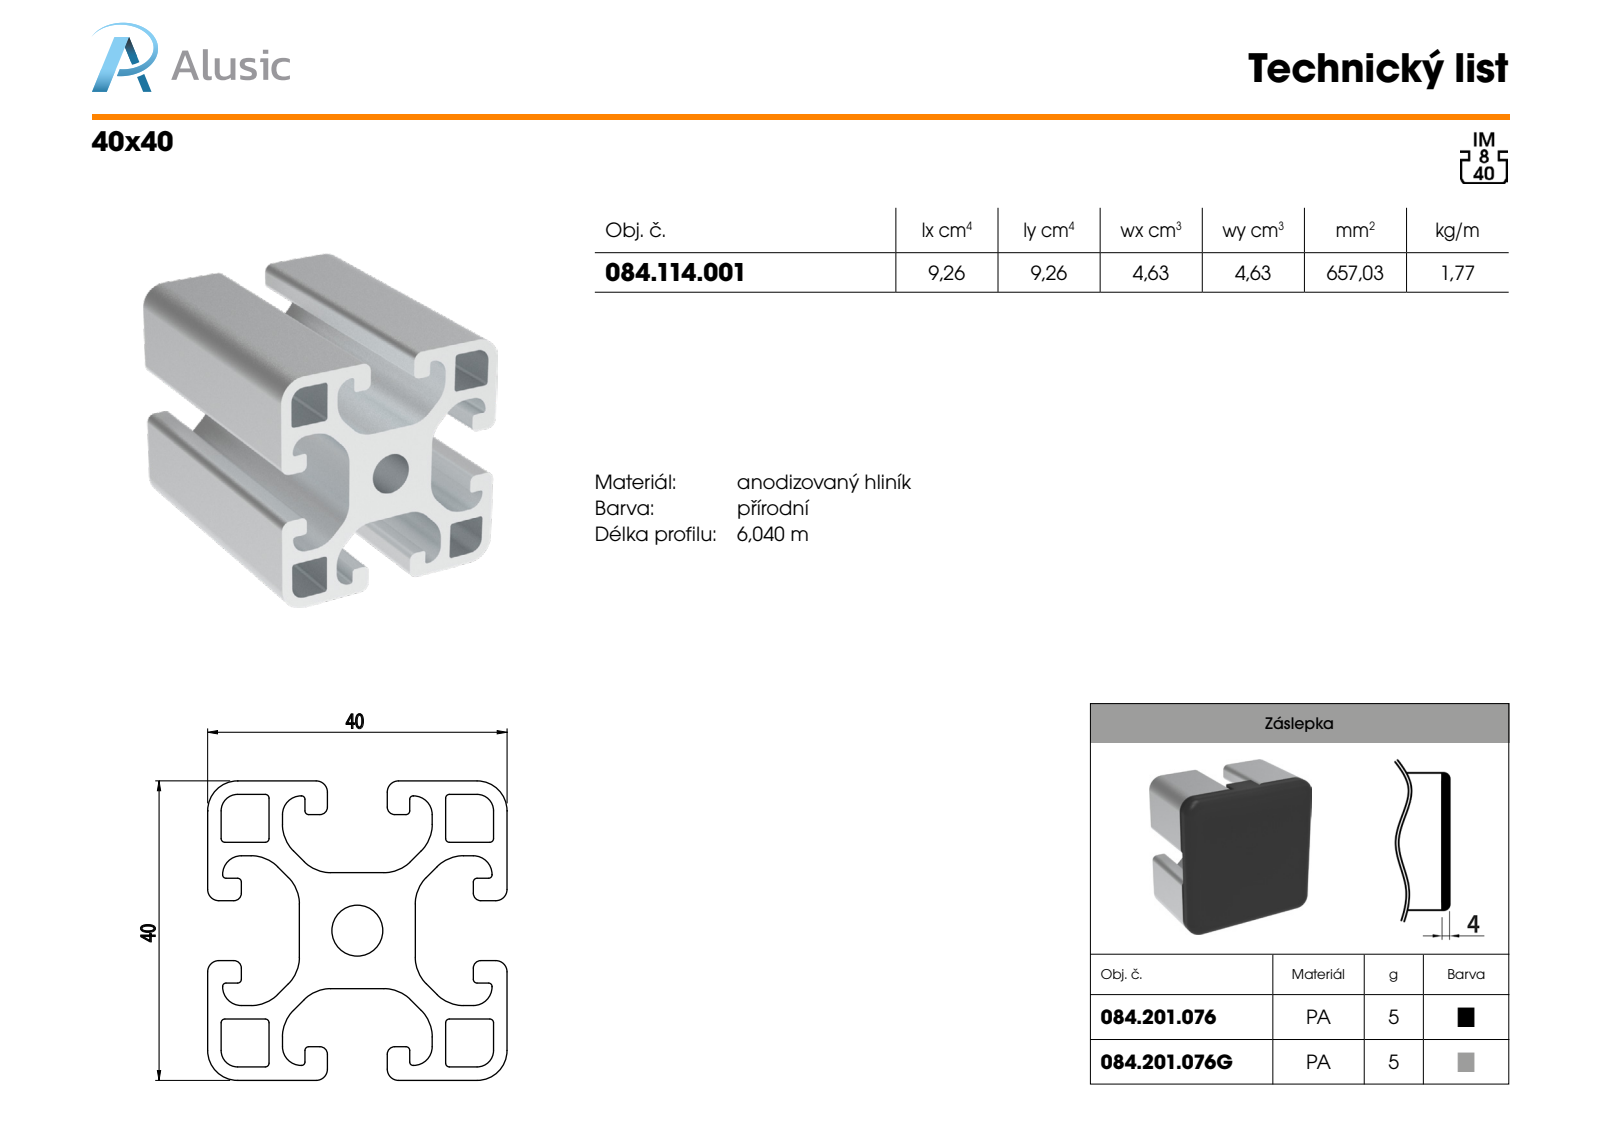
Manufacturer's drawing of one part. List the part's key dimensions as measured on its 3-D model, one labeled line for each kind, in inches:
Part name (STEP PRODUCT): 084.114.001
STEP written by: SolidWorks 2018 (AUTOMOTIVE_DESIGN)
Units: inches
Bodies: 1 solid, 155 faces (77 planar, 78 cylindrical, 0 other)
Overall size (bounding box): 3.937 × 1.575 × 1.575
Volume: 4.009 in³ · Surface area: 73.36 in²
Round holes (diameter × count): ⌀0.268 ×1
Partial cylindrical surfaces — rounded edges, fillets, slot ends (radius × count): R0.02 ×20, R0.197 ×16, R0.018 ×8, R0.039 ×8, R0.059 ×8, R0.098 ×8, R0.087 ×4, R0.157 ×4
Main face-to-face distances: 0.323, 1.252, 1.575, 1.181, 0.071, 0.118, 1.504, 0.252, 0.482, 1.093
